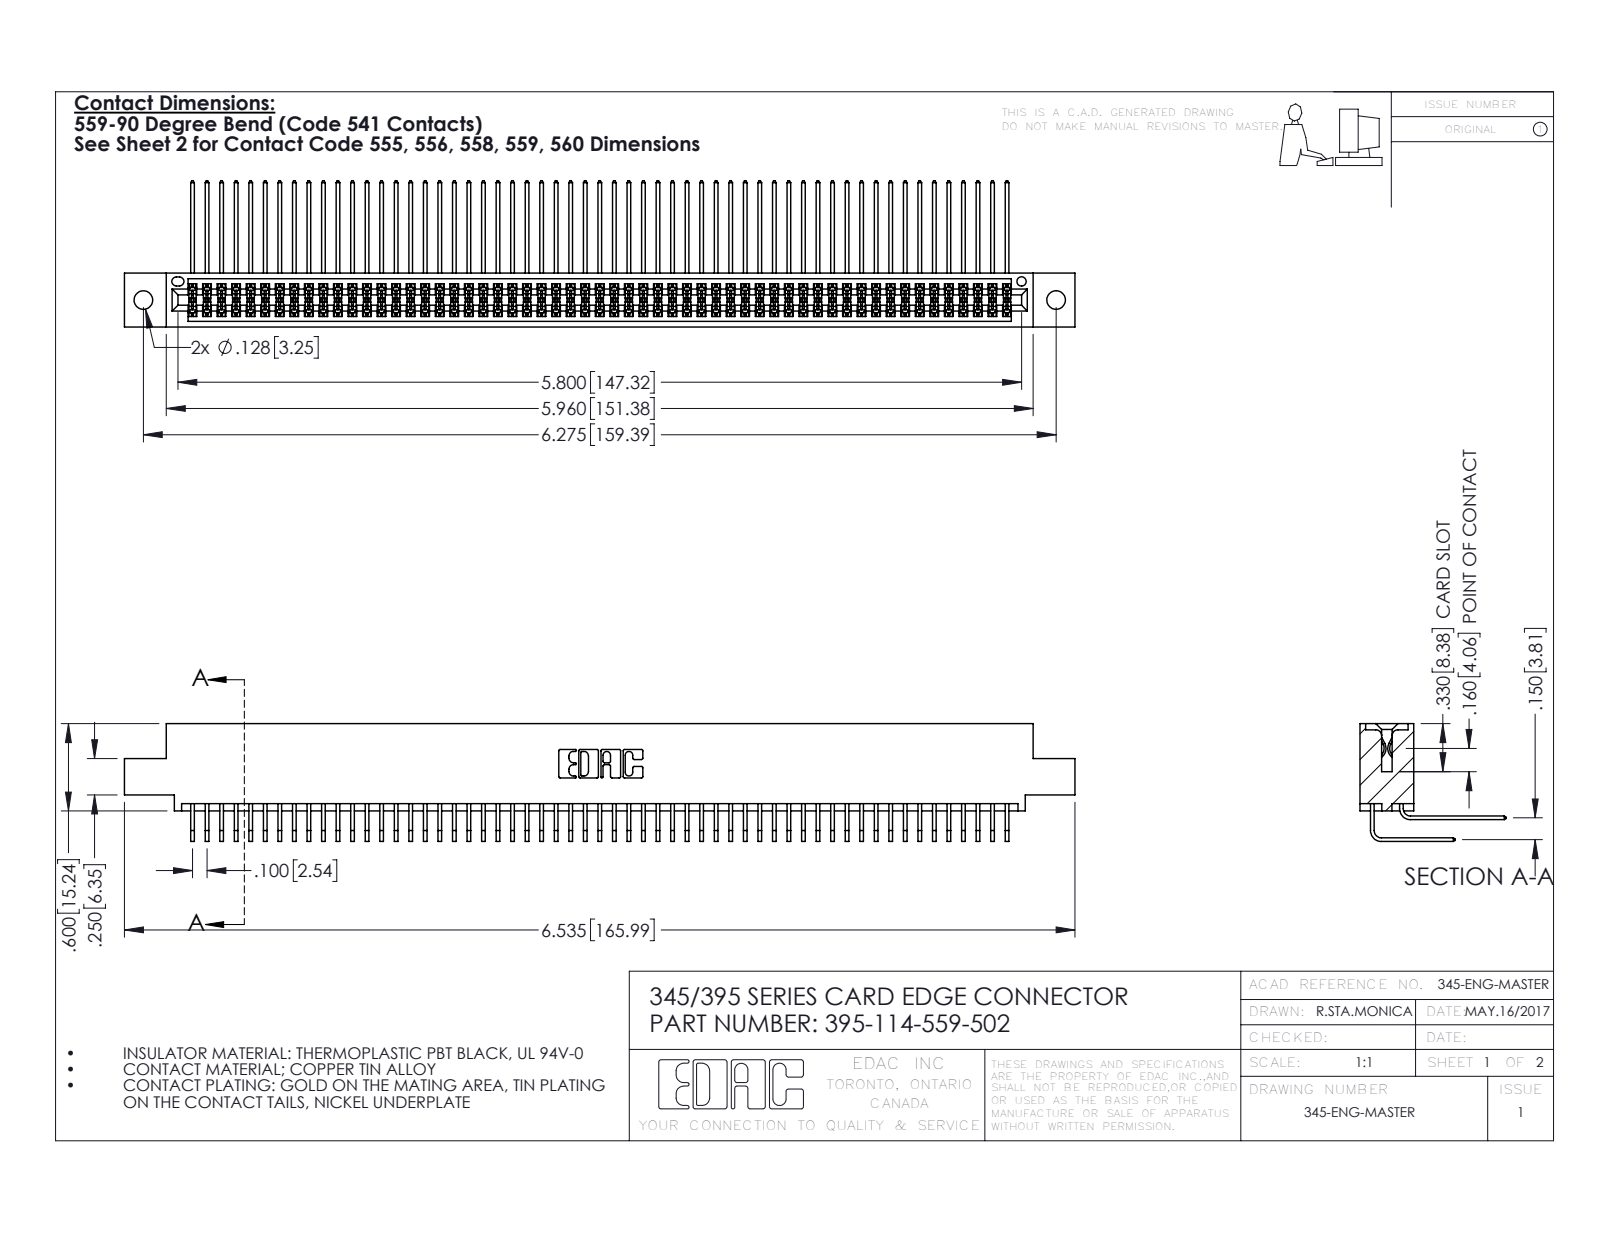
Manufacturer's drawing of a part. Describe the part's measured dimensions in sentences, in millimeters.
The part is named "345-292-001_559 Tail - 2; 345 Part_0.110 Offset - 0.128 Dia; 395-114-559-502; 345-292-001_558 559 Tail - 1". Its 3-D file was written by "SolidWorks 2016 (CONFIG_CONTROL_DESIGN)". It is 115 solids with 6058 faces: 4074 planar, 1984 cylindrical and 0 other. Overall it measures 166 by 25.5 by 20.5 millimeters. Its volume is 16 810 cubic millimeters and its surface area 28 050 square millimeters. Round holes: 2 of diameter 3.3, 1 of diameter 1.6. Partial cylindrical surfaces (rounded edges, fillets, slot ends): 171 of radius 0.2, 22 of radius 0.3, 6 of radius 0.2, 6 of radius 0.8, 3 of radius 0.7, 2 of radius 0.4, 2 of radius 0.5, 2 of radius 0.6. The main face-to-face distances are 1.8, 7.6, 5.1, 9.4, 2.5, 6.9, 0.6, 5.7, 4.4, 3.8. The hole center spacings are 6.9, 153.4, 159.4.
